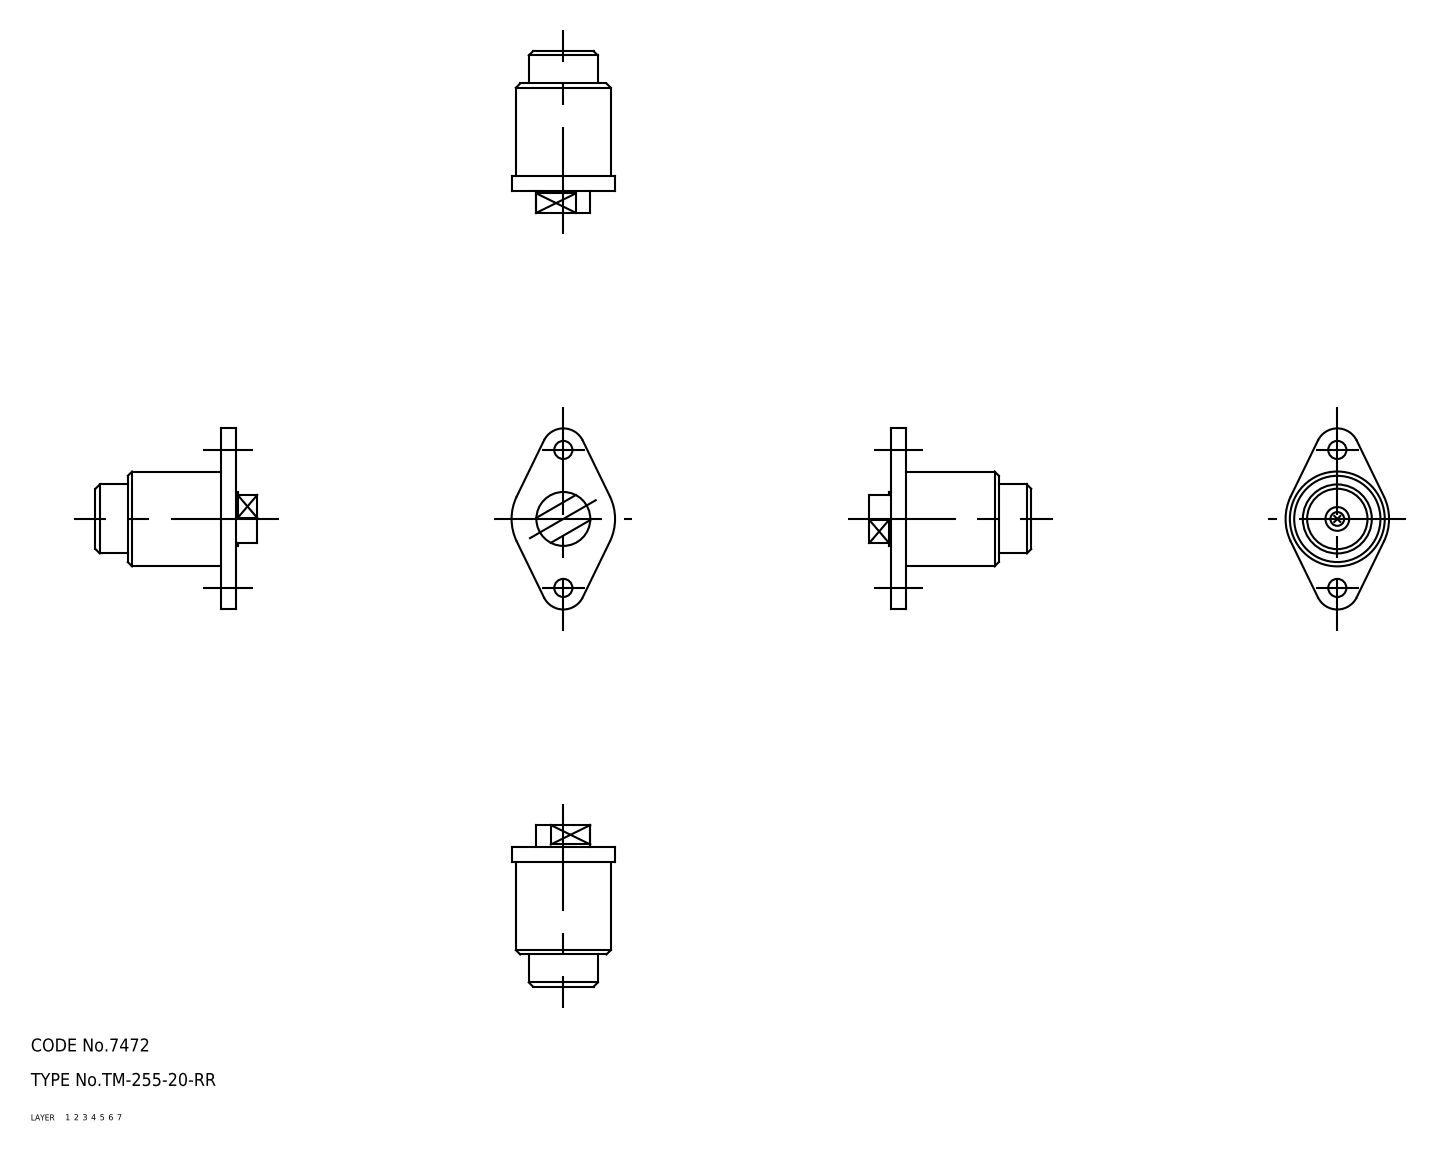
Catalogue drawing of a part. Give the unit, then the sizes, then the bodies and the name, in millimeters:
Units: millimetres
Overall size (bounding box): 42 × 37.5 × 24
Volume: 12 288 mm³ · Surface area: 4 263 mm²
Bodies: 2 solids, 56 faces (0 planar, 0 cylindrical, 56 other)
Part name (STEP PRODUCT): shaft_mr; housing; TM_255_20_RR_67_36
STEP written by: CADfix (AUTOMOTIVE_DESIGN)
